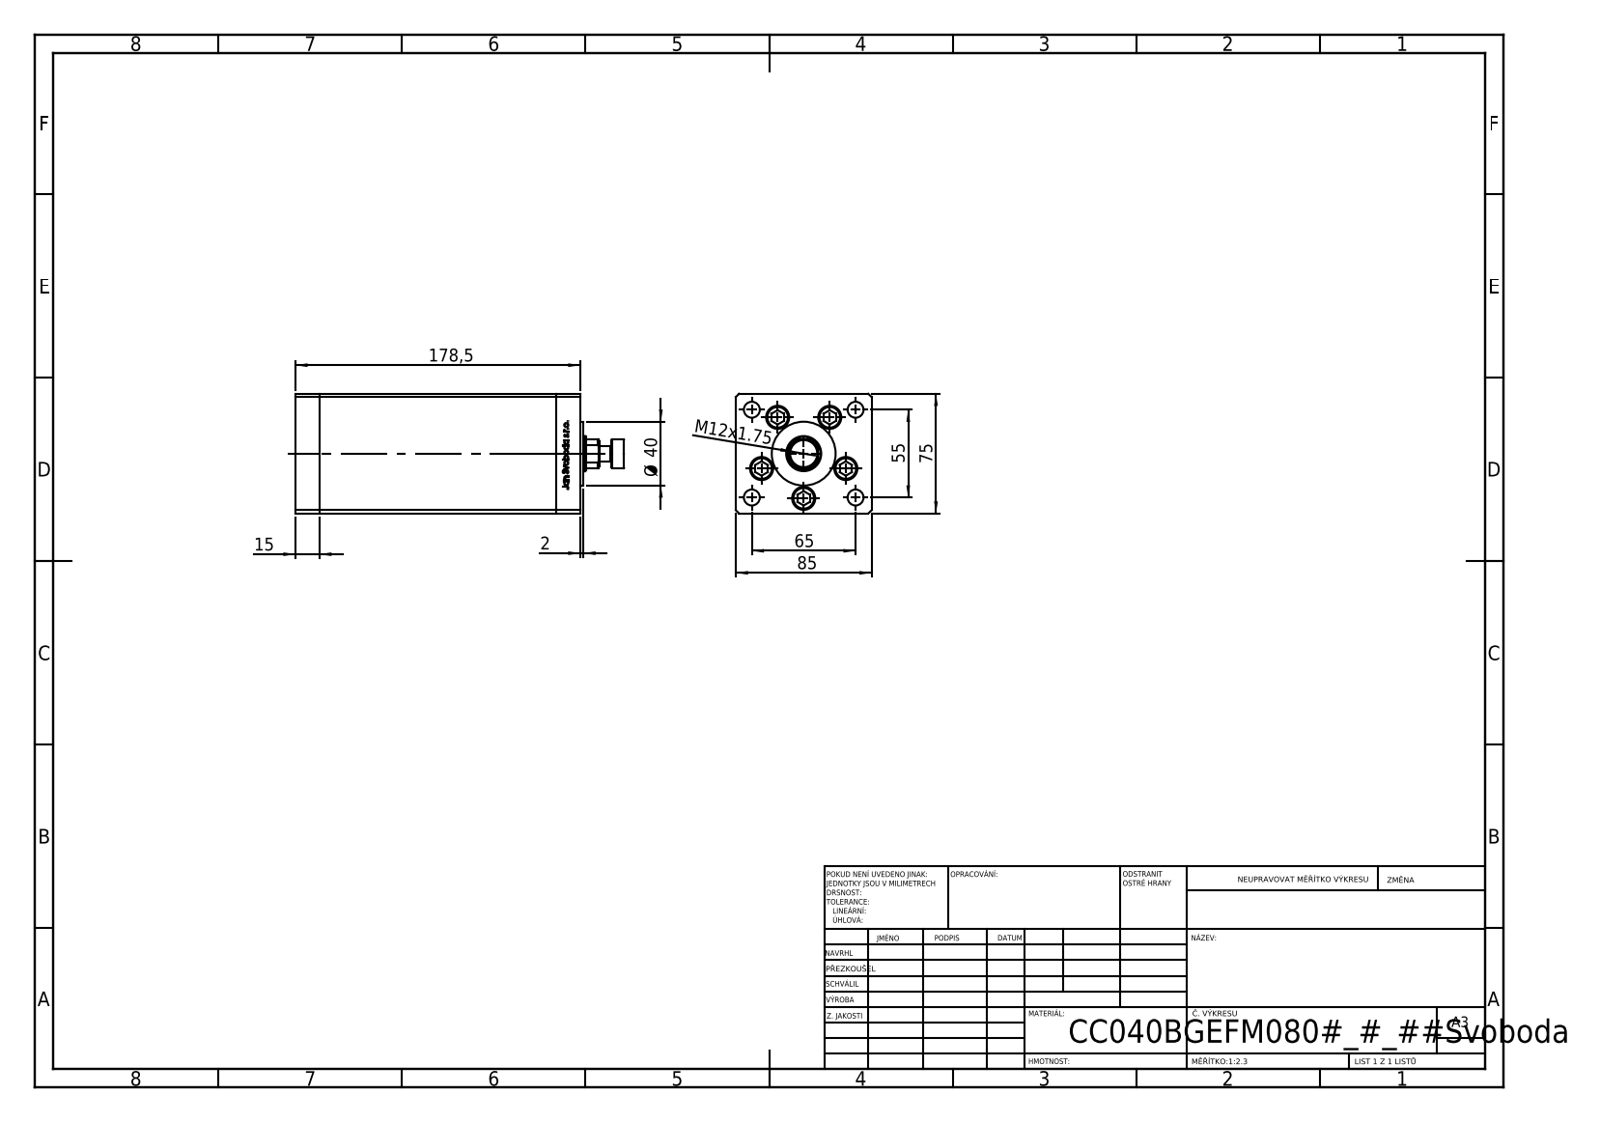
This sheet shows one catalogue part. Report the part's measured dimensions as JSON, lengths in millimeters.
{"part_name": "V220C_B MIDDLE; V220CC_FLOATING_JOINT; V220C_FRONT_B; V220C_VC_B (+2 more)", "step_written_by": "SolidWorks 2019 (CONFIG_CONTROL_DESIGN)", "units": "millimeters", "bodies": {"solids": 15, "faces": 1201, "planar": 468, "cylindrical": 151, "other": 582}, "overall_size": [206, 85, 75], "volume_mm3": 1014000, "surface_area_mm2": 161968, "round_holes": [[11, 5], [14.5, 5], [10, 4], [2, 2], [13.16, 2], [13.5, 1], [22, 1]], "round_bosses_or_shafts": [[8, 5], [40, 1], [18, 1], [10, 1]], "partial_cylinders_radius": [[0.93, 2], [10.5, 1]], "face_to_face_distances": [85, 75, 15, 148.5, 163.5, 178.5, 34.25, 19.25, 129.25, 144.25], "hole_center_spacings": [28, 42.57, 16.86, 19.17, 32.33, 32.5, 33.63, 37.33]}
